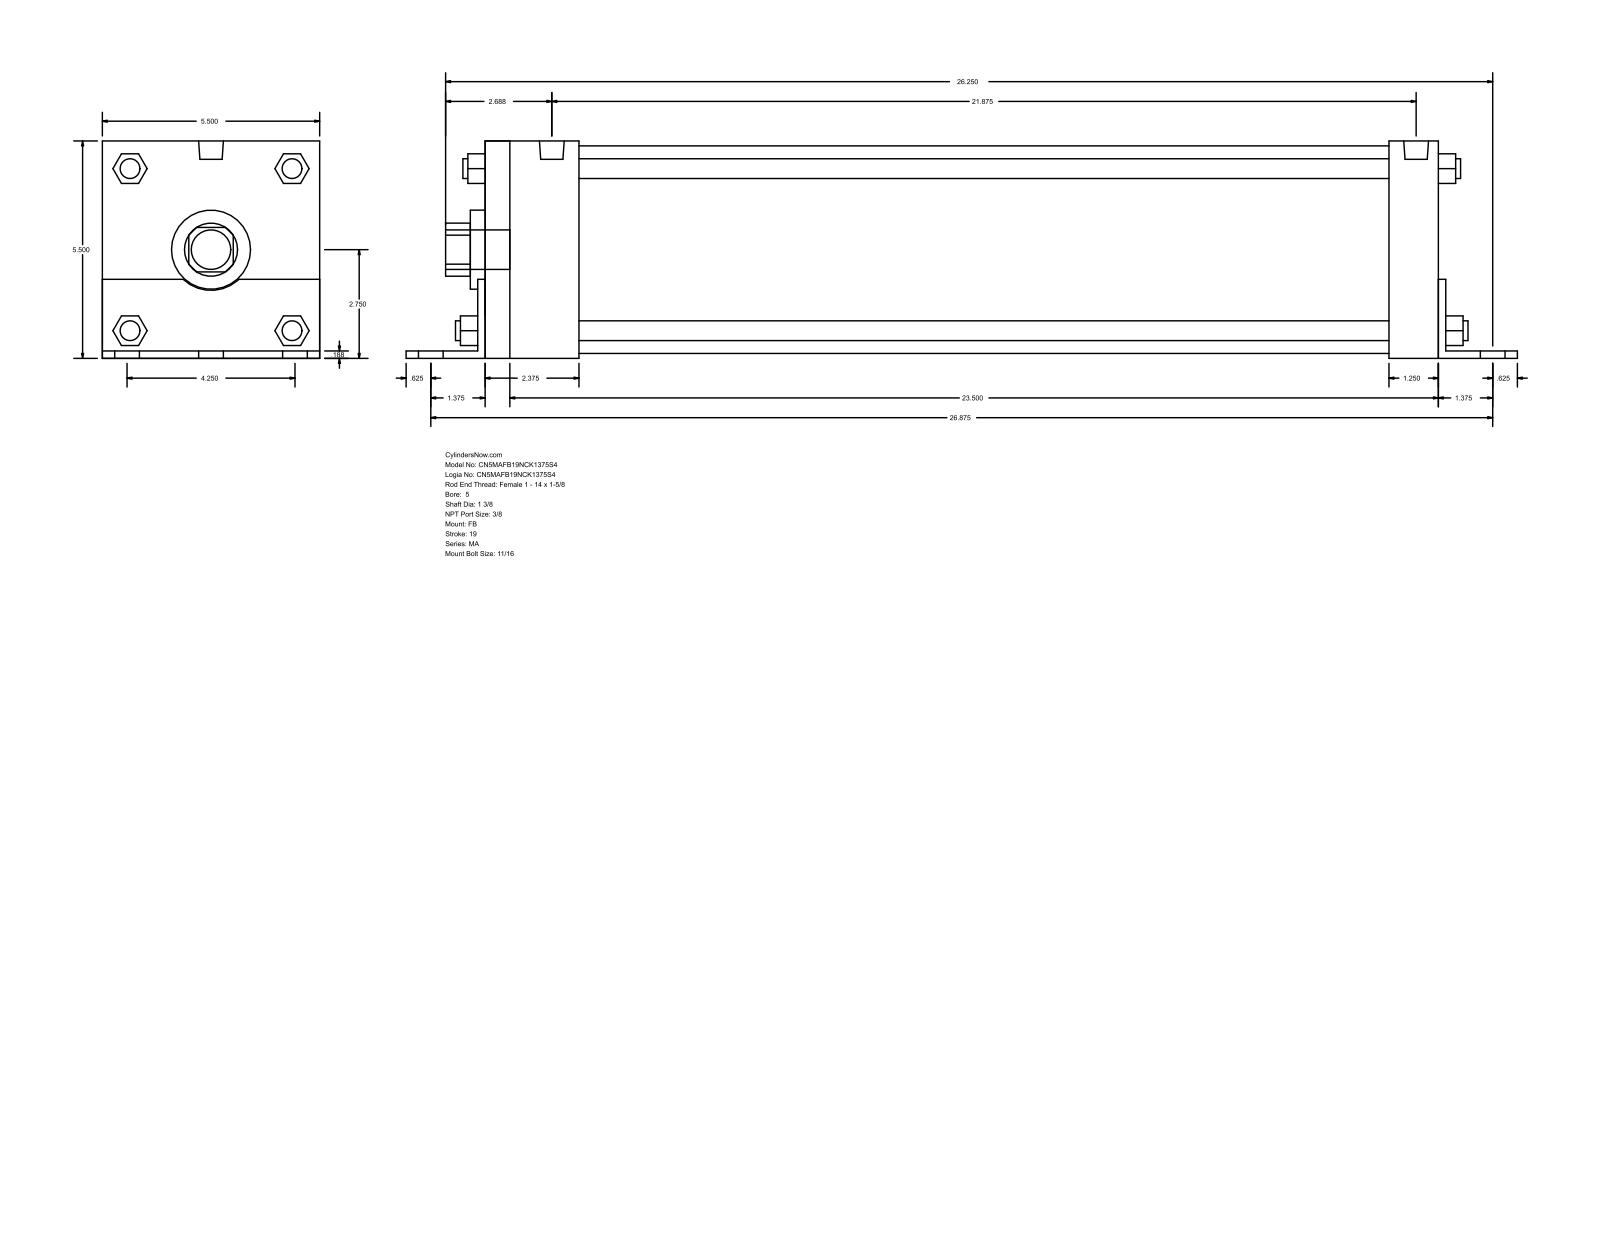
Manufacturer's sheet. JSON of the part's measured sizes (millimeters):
{"part_name": "MA_FB__0500_1.375", "step_written_by": "GSSL Pune (CONFIG_CONTROL_DESIGN)", "units": "millimeters", "bodies": {"solids": 0, "faces": 140, "planar": 105, "cylindrical": 35, "other": 0}, "overall_size": [714.38, 139.75, 139.7], "round_holes": [[34.92, 1], [50.8, 1], [133.35, 1]], "round_bosses_or_shafts": [[17.46, 6], [12.7, 4], [11.11, 4], [15.93, 2], [25.4, 1]], "partial_cylinders_radius": [[17.06, 1], [26.16, 1]], "face_to_face_distances": [139.7, 4.76, 139.75, 4.71, 134.99, 612.77, 4.77, 617.54, 617.53, 622.3]}
